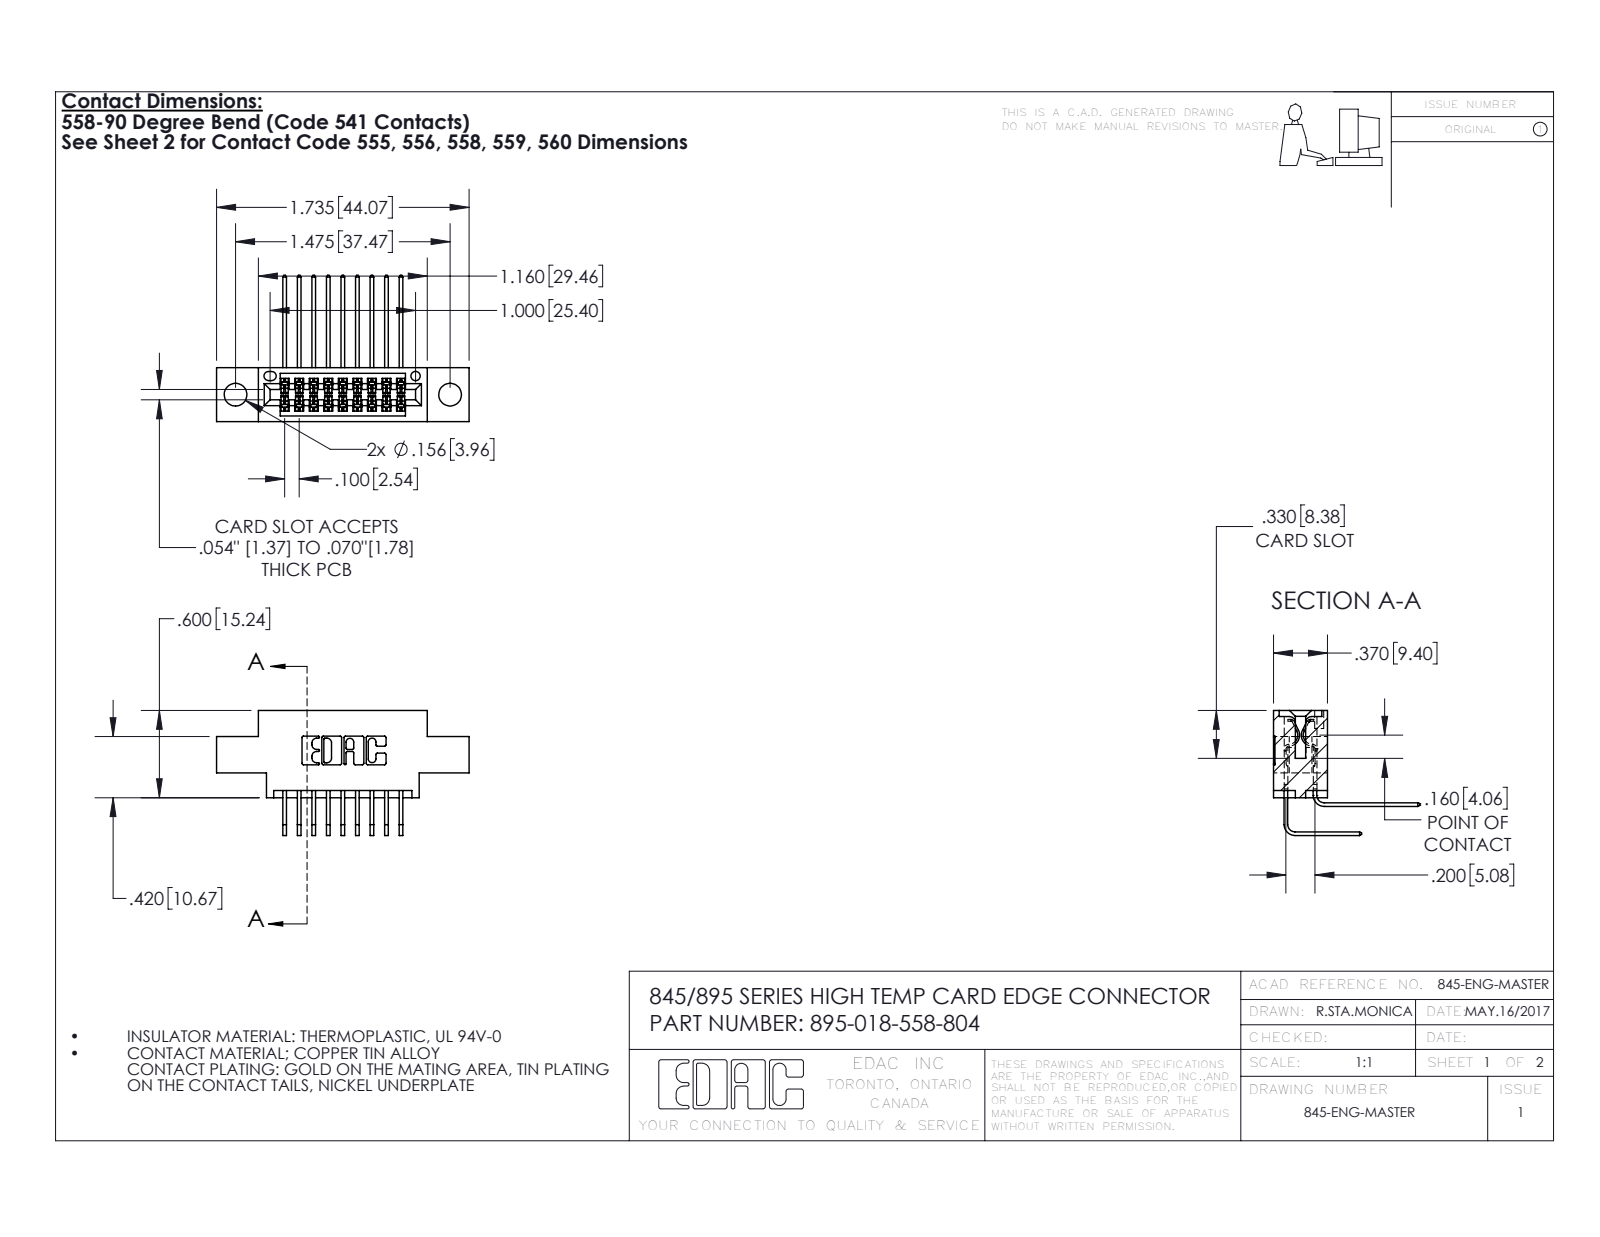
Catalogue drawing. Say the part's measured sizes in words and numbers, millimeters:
The part is named "345-292-001_558 559 Tail - 1; 345 Part_0.170 Offset - 0.156 Dia-TH; 345-292-001_558 Tail - 2; 395-018-558-804". Its 3-D file was written by "SolidWorks 2016 (CONFIG_CONTROL_DESIGN)". It is 19 solids with 1066 faces: 714 planar, 352 cylindrical and 0 other. Overall it measures 44.1 by 25.5 by 21.8 millimeters. Its volume is 3 880 cubic millimeters and its surface area 5 539 square millimeters. Round holes: 2 of diameter 4, 1 of diameter 1.6. Partial cylindrical surfaces (rounded edges, fillets, slot ends): 36 of radius 0.2, 22 of radius 0.3, 6 of radius 0.2, 6 of radius 0.8, 3 of radius 0.7, 2 of radius 0.4, 2 of radius 0.5, 2 of radius 0.6. The main face-to-face distances are 5.1, 9.4, 1.8, 7.6, 2.5, 6.9, 0.6, 2.5, 5.7, 7.6. The hole center spacings are 6.9, 31.6, 37.5.
